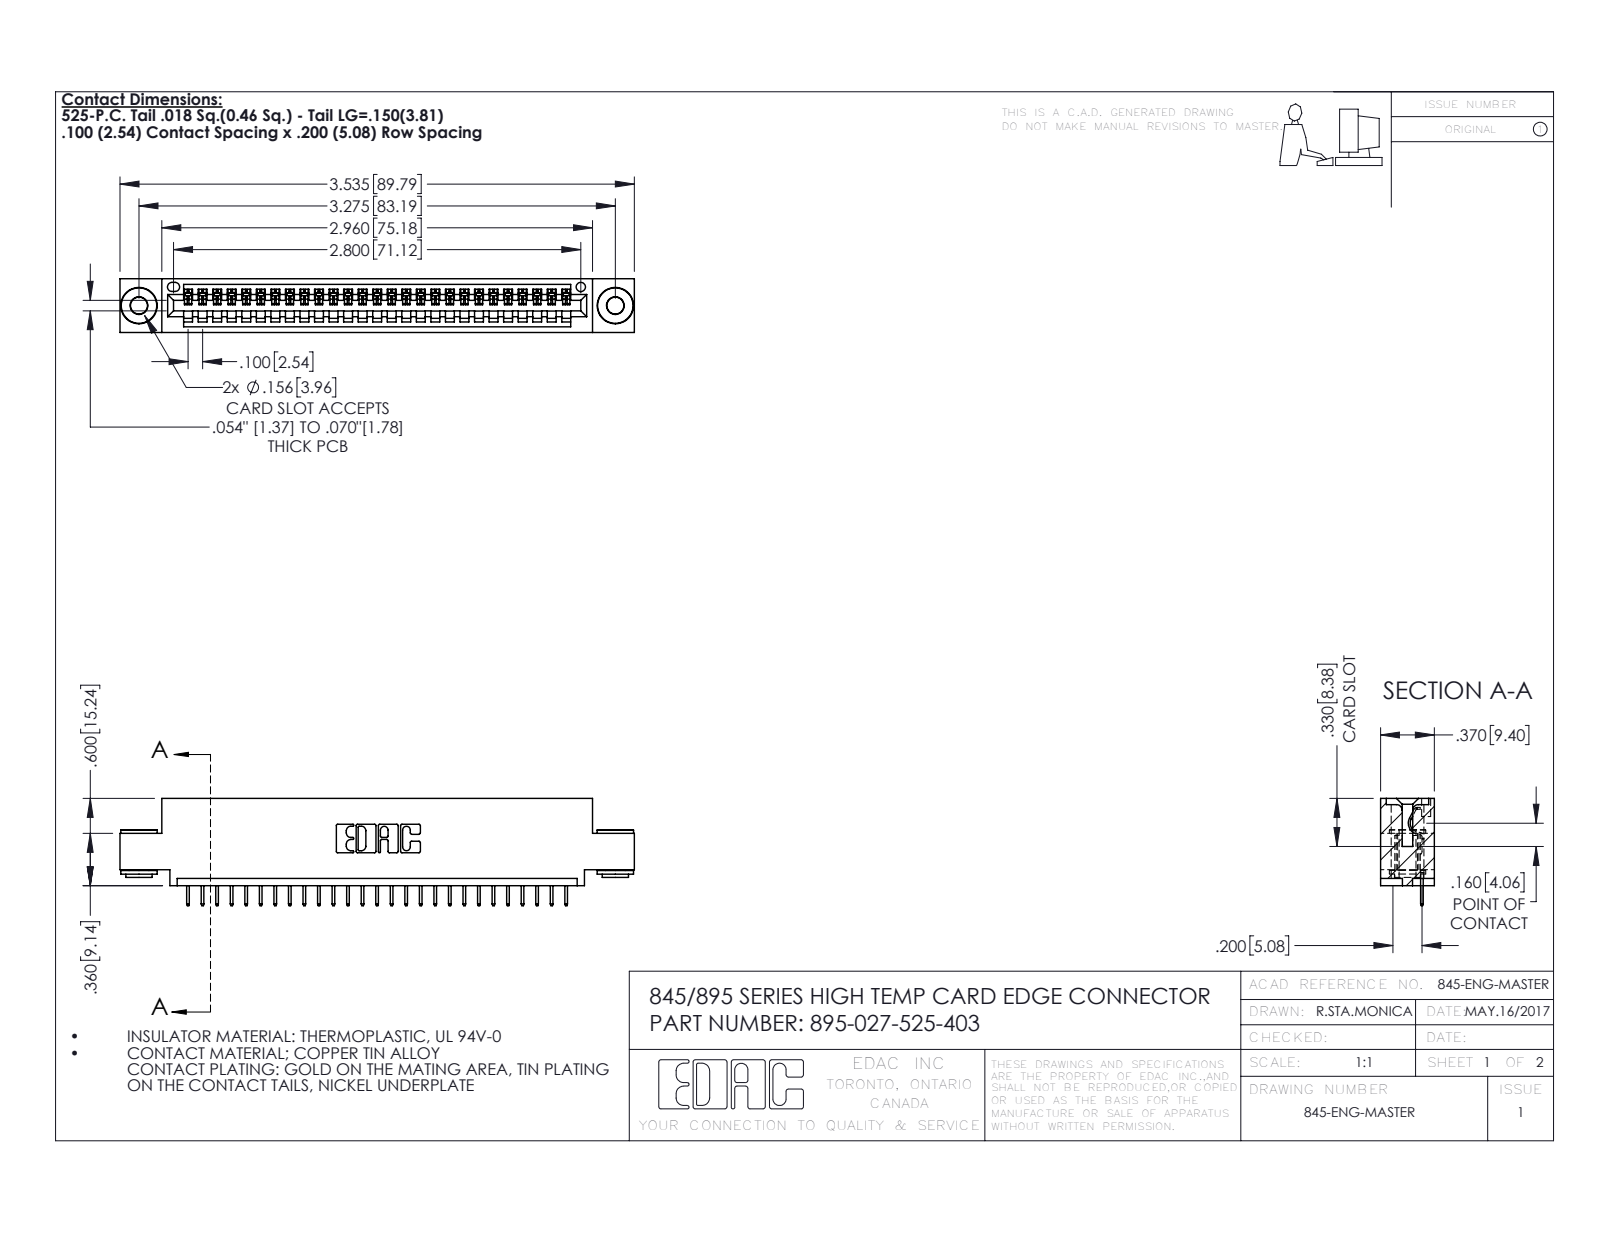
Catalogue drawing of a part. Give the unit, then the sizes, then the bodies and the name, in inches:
Units: inches
Overall size (bounding box): 3.535 × 0.737 × 0.37
Round holes (diameter × count): ⌀0.116 ×2, ⌀0.156 ×2, ⌀0.064 ×1
Round bosses / shafts (diameter × count): ⌀0.25 ×2, ⌀0.18 ×2, ⌀0.136 ×2
Partial cylindrical surfaces — rounded edges, fillets, slot ends (radius × count): R0.006 ×54, R0.01 ×22, R0.007 ×6, R0.031 ×6, R0.026 ×3, R0.031 ×2, R0.04 ×2, R0.014 ×1
Main face-to-face distances: 0.072, 0.298, 0.37, 0.2, 0.025, 0.098, 0.272, 0.225, 0.072, 0.149
Hole centre spacings: 0.27, 3.04, 3.275
Volume: 0.503 in³ · Surface area: 16.55 in²
Bodies: 30 solids, 1842 faces (1336 planar, 498 cylindrical, 8 other)
Part name (STEP PRODUCT): 895-027-525-403; 345-250-002_345-250-002-102; 845 Part_0.110 Offset - 0.156 Dia-TH; 345-292-001_345-293-125
STEP written by: SolidWorks 2020 (CONFIG_CONTROL_DESIGN)
